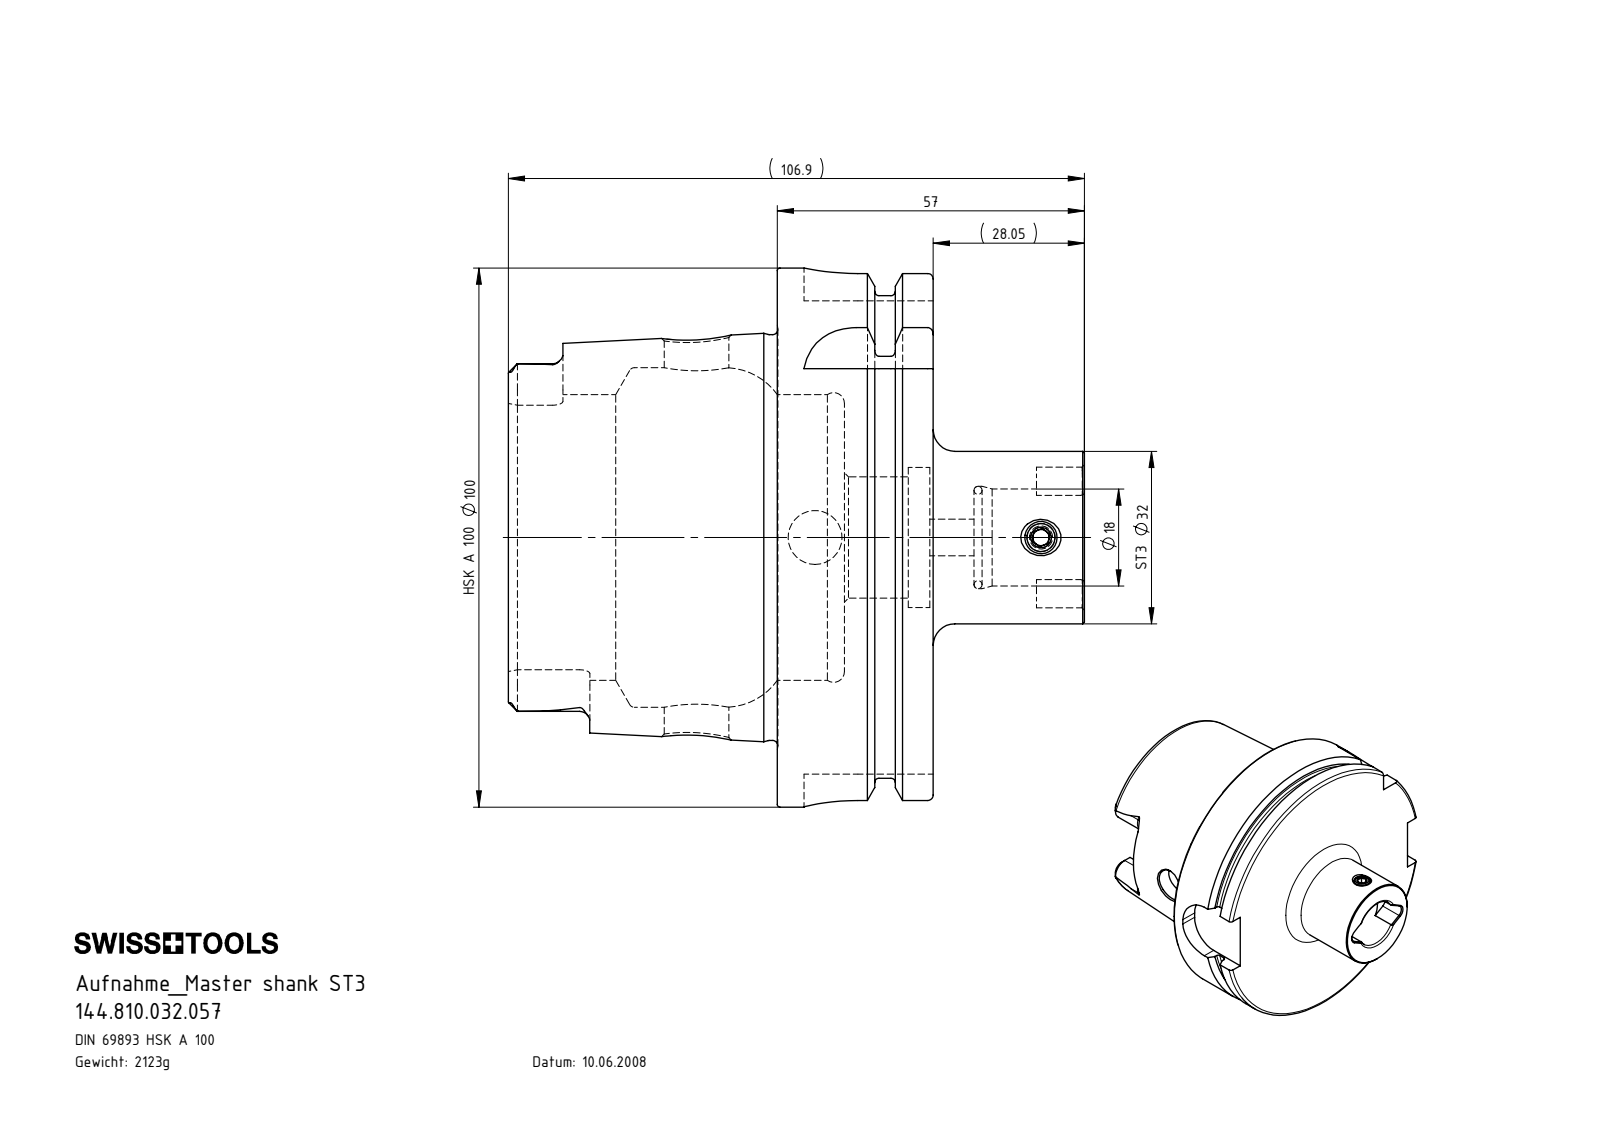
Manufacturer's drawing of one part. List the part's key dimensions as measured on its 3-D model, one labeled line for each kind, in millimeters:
Part name (STEP PRODUCT): DIN 3771 - 16x1.5; HA0.ST3.K01.057; HA0-ST3.K01.057_B_Fertigbearbeitung; ST3-ER1.001.008_A
STEP written by: SolidWorks 2017 (AUTOMOTIVE_DESIGN)
Units: millimetres
Bodies: 3 solids, 159 faces (63 planar, 39 cylindrical, 57 other)
Overall size (bounding box): 106.9 × 100 × 100
Volume: 270 385 mm³ · Surface area: 54 173 mm²
Round holes (diameter × count): ⌀3 ×1, ⌀5.25 ×1, ⌀6.8 ×1, ⌀10 ×1, ⌀12 ×1, ⌀18 ×1, ⌀19 ×1, ⌀22.5 ×1, ⌀26 ×1, ⌀53 ×1, ⌀63 ×1
Round bosses / shafts (diameter × count): ⌀100 ×1, ⌀91.95 ×1, ⌀75.26 ×1, ⌀32 ×1, ⌀6 ×1
Partial cylindrical surfaces — rounded edges, fillets, slot ends (radius × count): R1.9 ×6, R4.88 ×4, R10 ×4, R2.5 ×2
Main face-to-face distances: 28.95, 12.45, 16.5, 49.9, 62.35, 78.85, 78.2, 28.3, 15.85, 0.65
Hole centre spacings: 41.95
